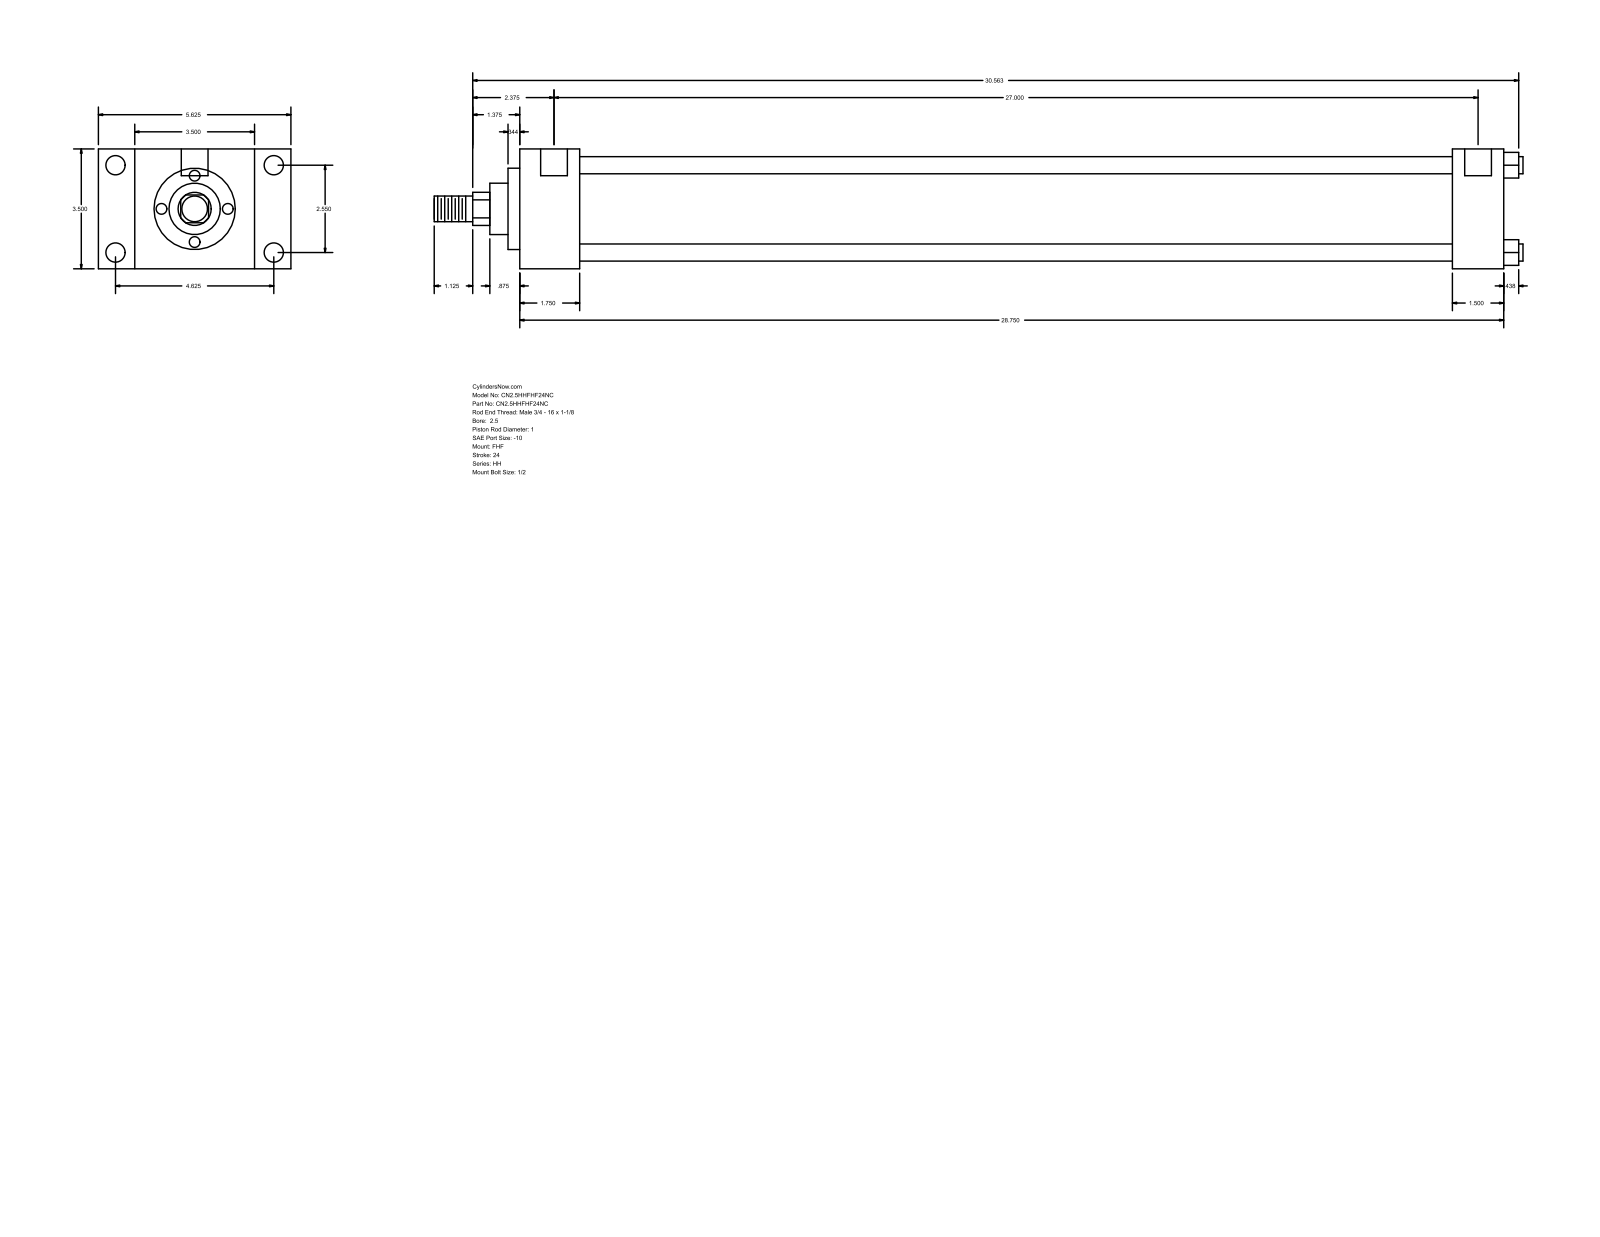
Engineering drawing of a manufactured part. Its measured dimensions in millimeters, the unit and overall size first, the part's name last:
Units: millimetres
Overall size (bounding box): 808.04 × 142.88 × 88.9
Round holes (diameter × count): ⌀5.56 ×4, ⌀14.3 ×4, ⌀19.84 ×2
Round bosses / shafts (diameter × count): ⌀12.7 ×4, ⌀73.03 ×1, ⌀60.33 ×1, ⌀38.1 ×1, ⌀25.4 ×1, ⌀19.05 ×1
Partial cylindrical surfaces — rounded edges, fillets, slot ends (radius × count): R12.29 ×1
Main face-to-face distances: 88.9, 44.46, 26.99, 115.89, 730.25, 685.79, 142.88, 692.16, 647.7, 38.09
Hole centre spacings: 1.59, 64.76, 117.48, 134.15, 687.38, 688.97, 685.79
Bodies: 0 solids, 90 faces (61 planar, 29 cylindrical, 0 other)
Part name (STEP PRODUCT): HH_FHF__0250_1
STEP written by: GSSL Pune (CONFIG_CONTROL_DESIGN)
